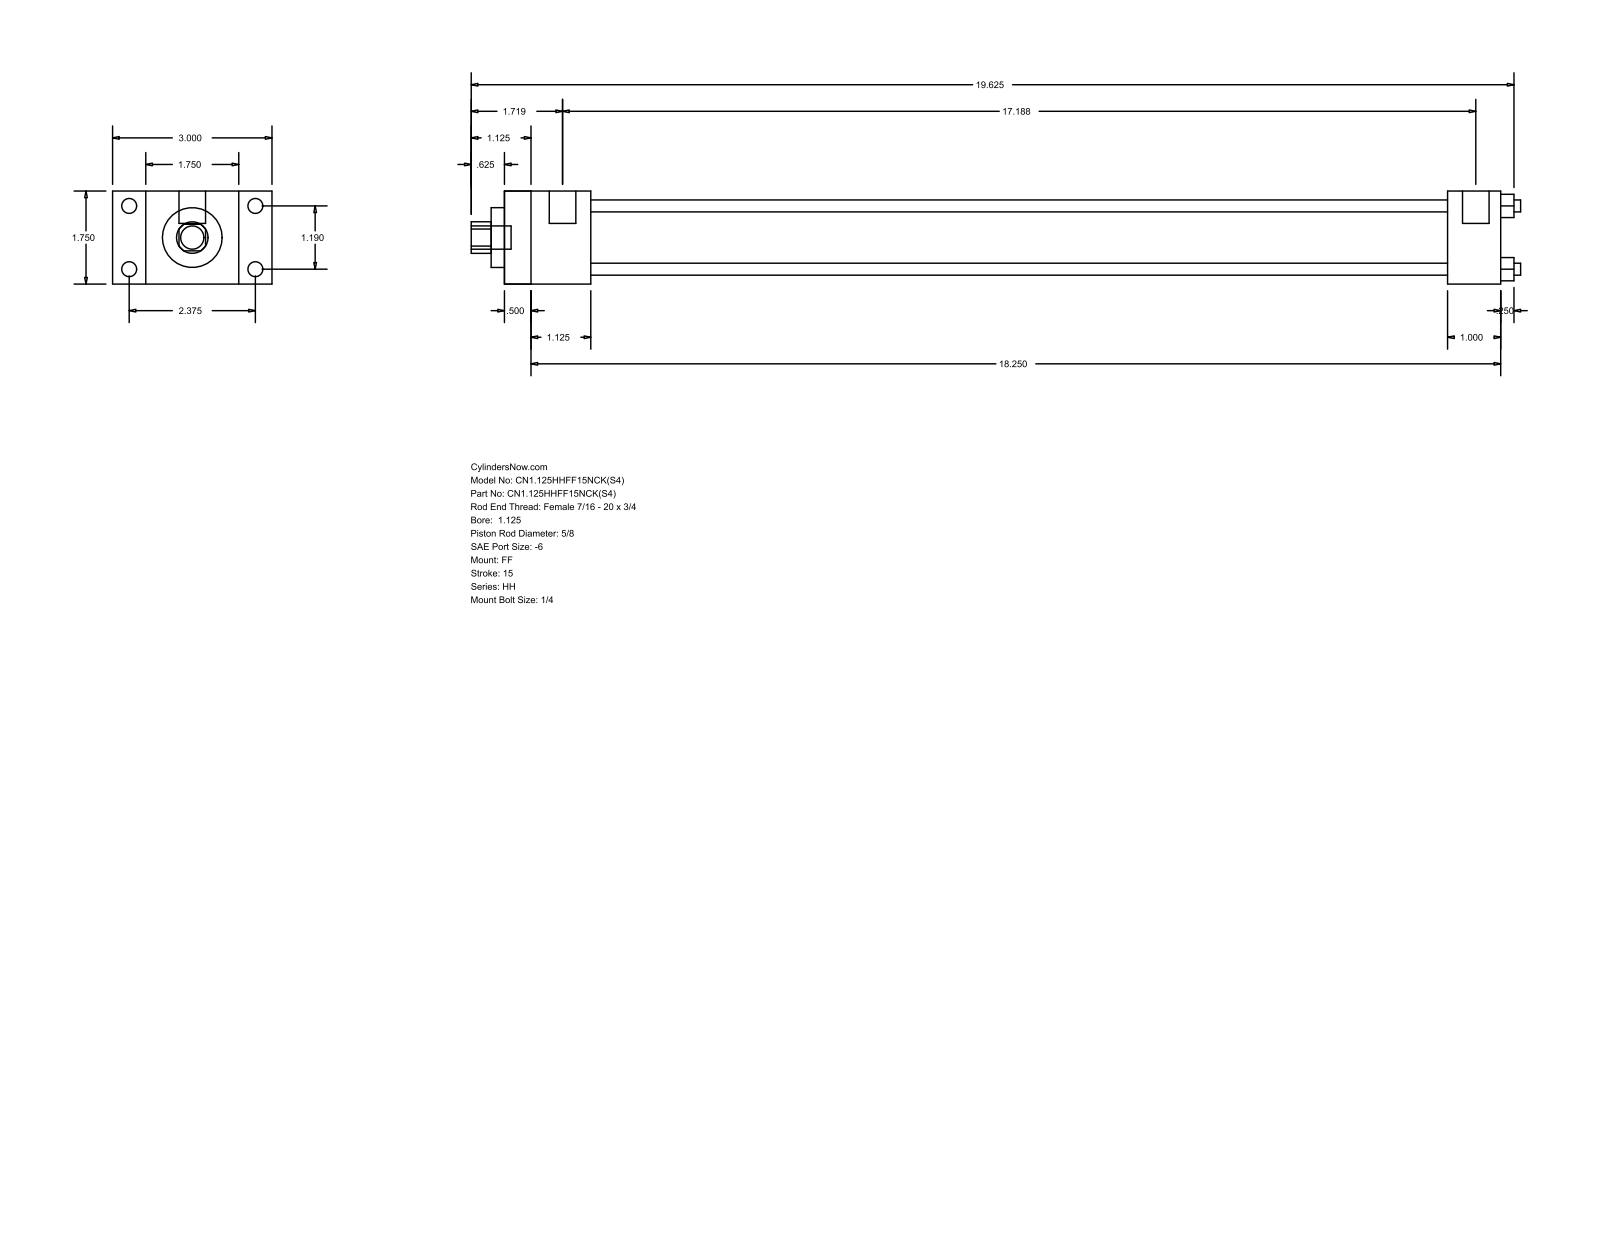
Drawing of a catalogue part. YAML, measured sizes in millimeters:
part_name: "HH_FF__0112_0.625"
step_written_by: "GSSL Pune (CONFIG_CONTROL_DESIGN)"
units: millimeters
bodies: {solids: 0, faces: 92, planar: 64, cylindrical: 28, other: 0}
overall_size: [501.65, 76.2, 44.45]
round_holes:
  - {diameter: 5.71, count: 4}
  - {diameter: 15.88, count: 1}
  - {diameter: 28.57, count: 1}
  - {diameter: 34.92, count: 1}
round_bosses_or_shafts:
  - {diameter: 7.14, count: 4}
  - {diameter: 5.56, count: 4}
  - {diameter: 12.7, count: 2}
  - {diameter: 11.11, count: 1}
partial_cylinders:
  - {radius: 7.54, count: 1}
face_to_face_distances: [44.46, 476.24, 15.87, 12.69, 463.55, 60.33, 28.58, 41.27, 450.85, 438.16]
hole_center_spacings: [21.37, 30.22, 42.74]
